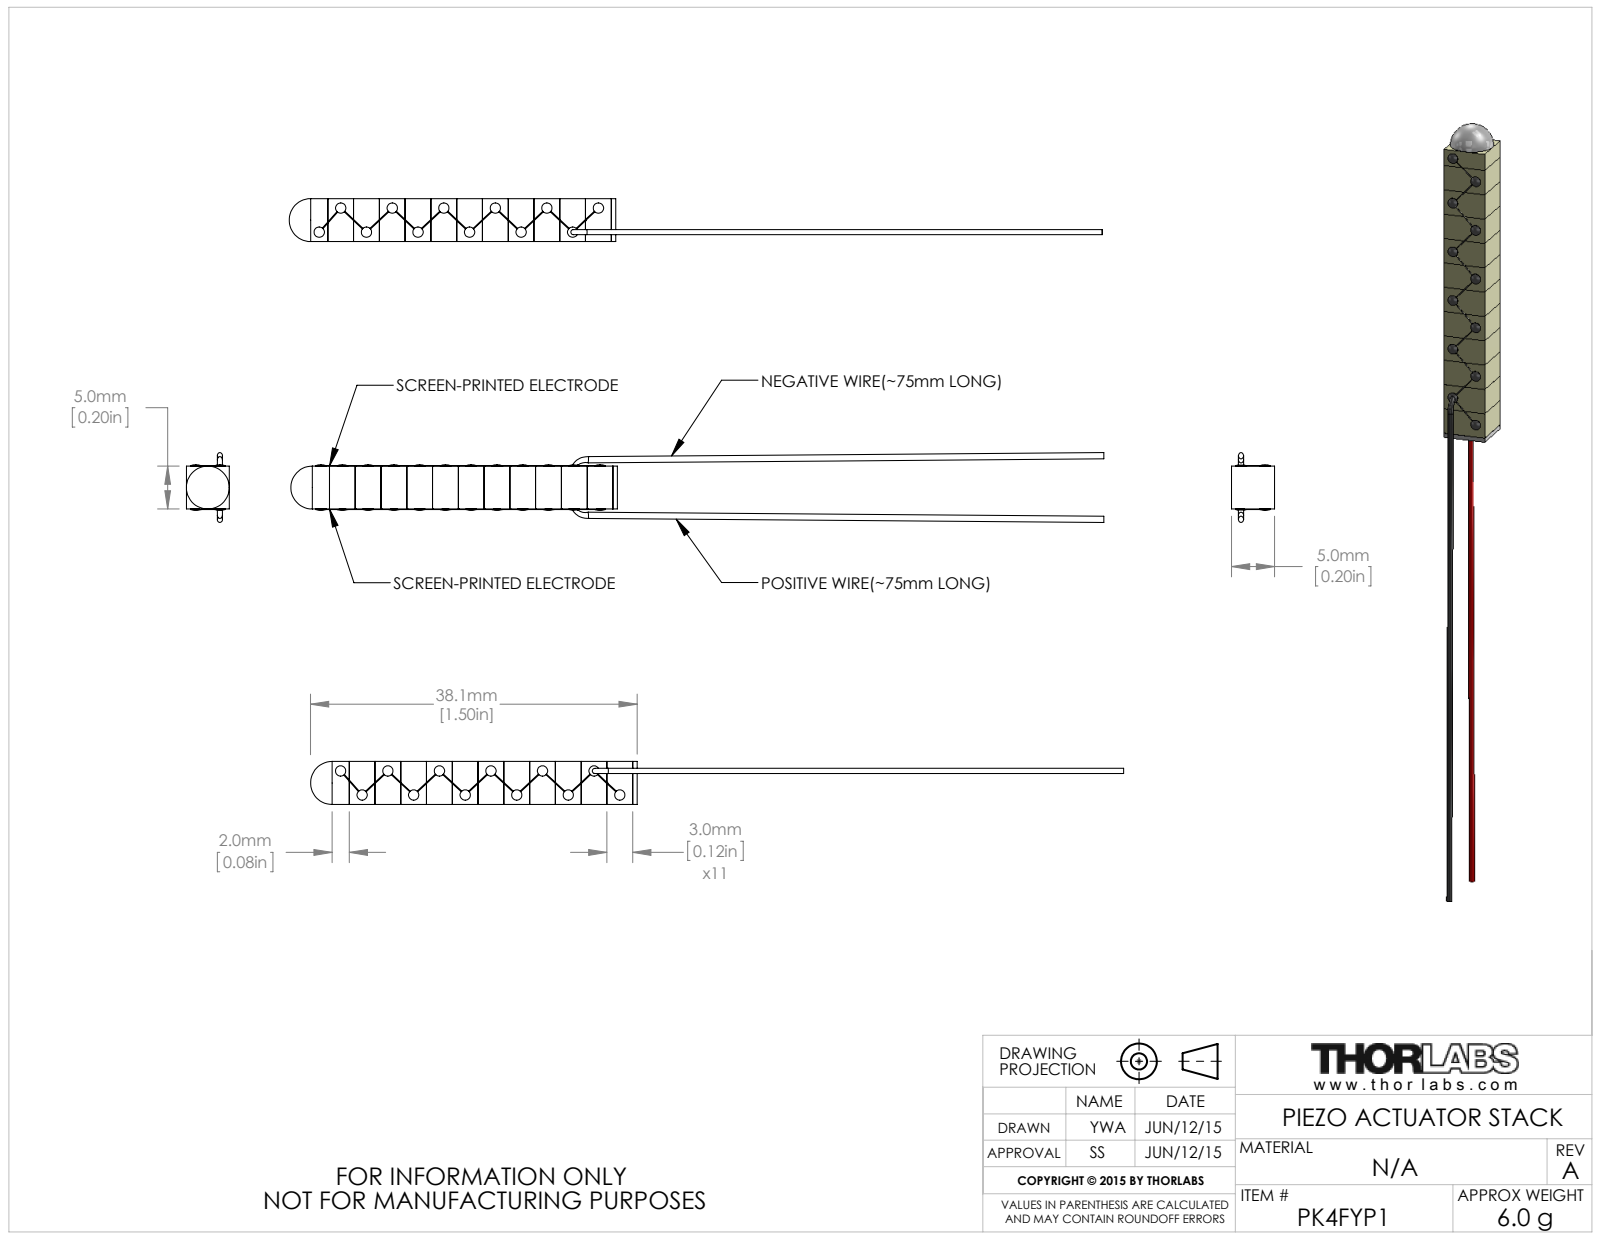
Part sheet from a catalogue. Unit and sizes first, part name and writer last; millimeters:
Units: millimetres
Overall size (bounding box): 94.65 × 8.12 × 5
Round bosses / shafts (diameter × count): ⌀1.2 ×12
Main face-to-face distances: 3, 6, 9, 12, 5, 15, 18, 21, 24, 27
Volume: 965 mm³ · Surface area: 1 719 mm²
Bodies: 31 solids, 265 faces (115 planar, 92 cylindrical, 58 other)
Part name (STEP PRODUCT): CTN002967
STEP written by: SolidWorks 2014 (AUTOMOTIVE_DESIGN)
